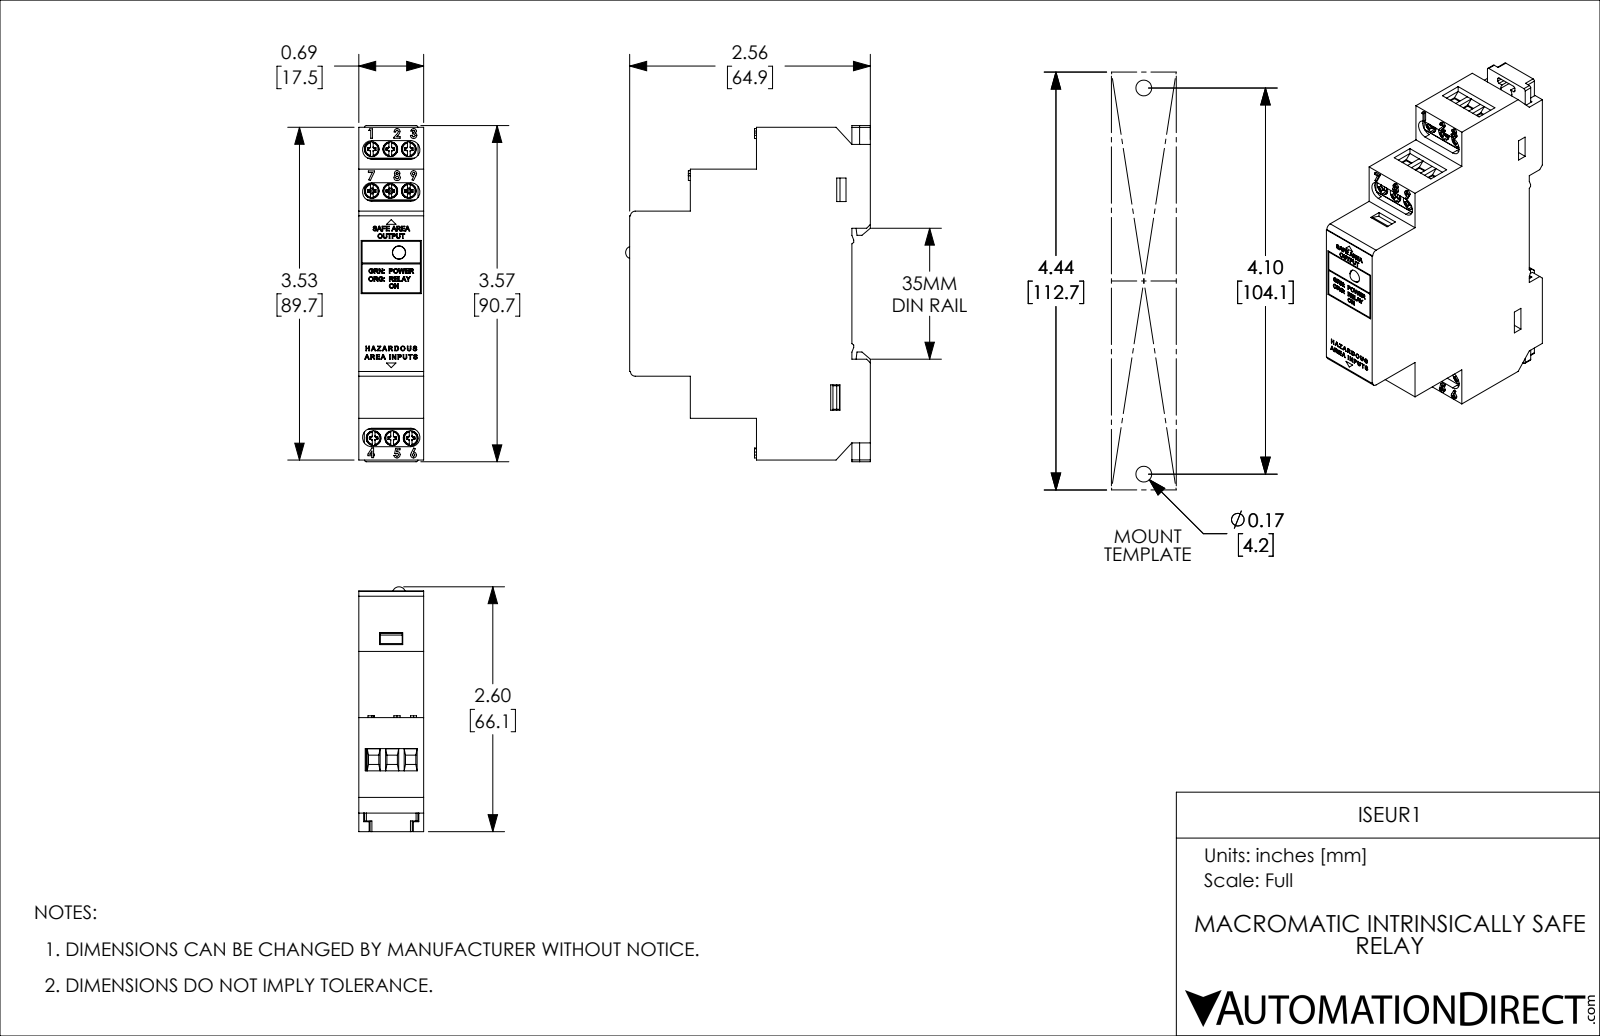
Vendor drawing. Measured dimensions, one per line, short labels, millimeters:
name: ISEUR1
written by: SolidWorks 2019 (AUTOMOTIVE_DESIGN)
unit: mm
bodies: 2 solids, 1290 faces (956 planar, 6 cylindrical, 328 other)
size: 90.7 × 66 × 17.5
volume: 75 120 mm³; area: 19 770 mm²
holes: 1× ⌀3.6
bosses: 1× ⌀3.5
face distances: 17.5, 59.9, 11.4, 5, 64.9, 11.3, 78.5, 22.6, 67.1, 55.9
